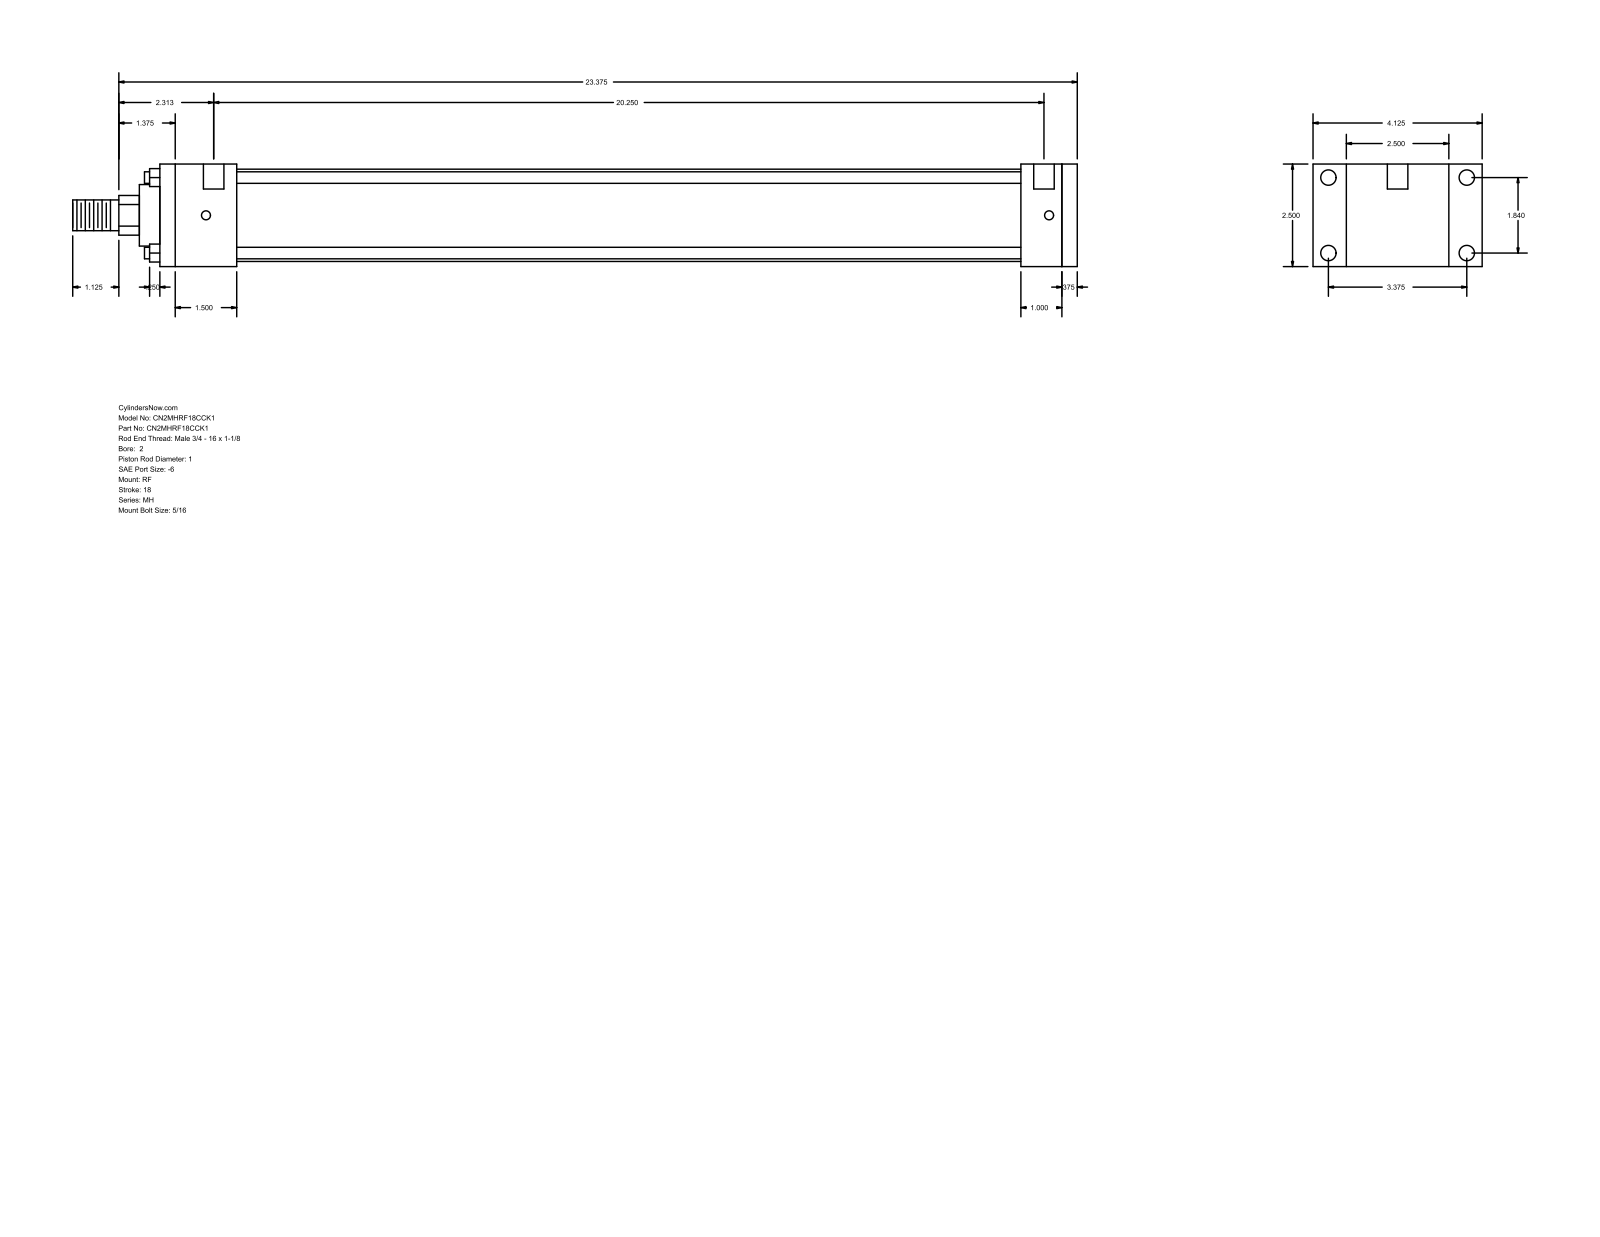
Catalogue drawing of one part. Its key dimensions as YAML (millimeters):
part_name: "MH_RF__0200_1"
step_written_by: "GSSL Pune (CONFIG_CONTROL_DESIGN)"
units: millimeters
bodies: {solids: 0, faces: 92, planar: 64, cylindrical: 28, other: 0}
overall_size: [622.3, 104.78, 63.5]
round_holes:
  - {diameter: 5.56, count: 4}
  - {diameter: 9.53, count: 4}
  - {diameter: 12.7, count: 2}
round_bosses_or_shafts:
  - {diameter: 7.14, count: 4}
  - {diameter: 57.15, count: 1}
  - {diameter: 38.1, count: 1}
  - {diameter: 25.4, count: 1}
  - {diameter: 19.05, count: 1}
partial_cylinders:
  - {radius: 12.29, count: 1}
face_to_face_distances: [63.5, 568.33, 558.8, 9.53, 20.64, 25.4, 47.63, 533.4, 485.77, 511.17]
hole_center_spacings: [46.74, 85.72, 97.63, 522.28, 3.17, 4.76, 514.35, 517.52]
